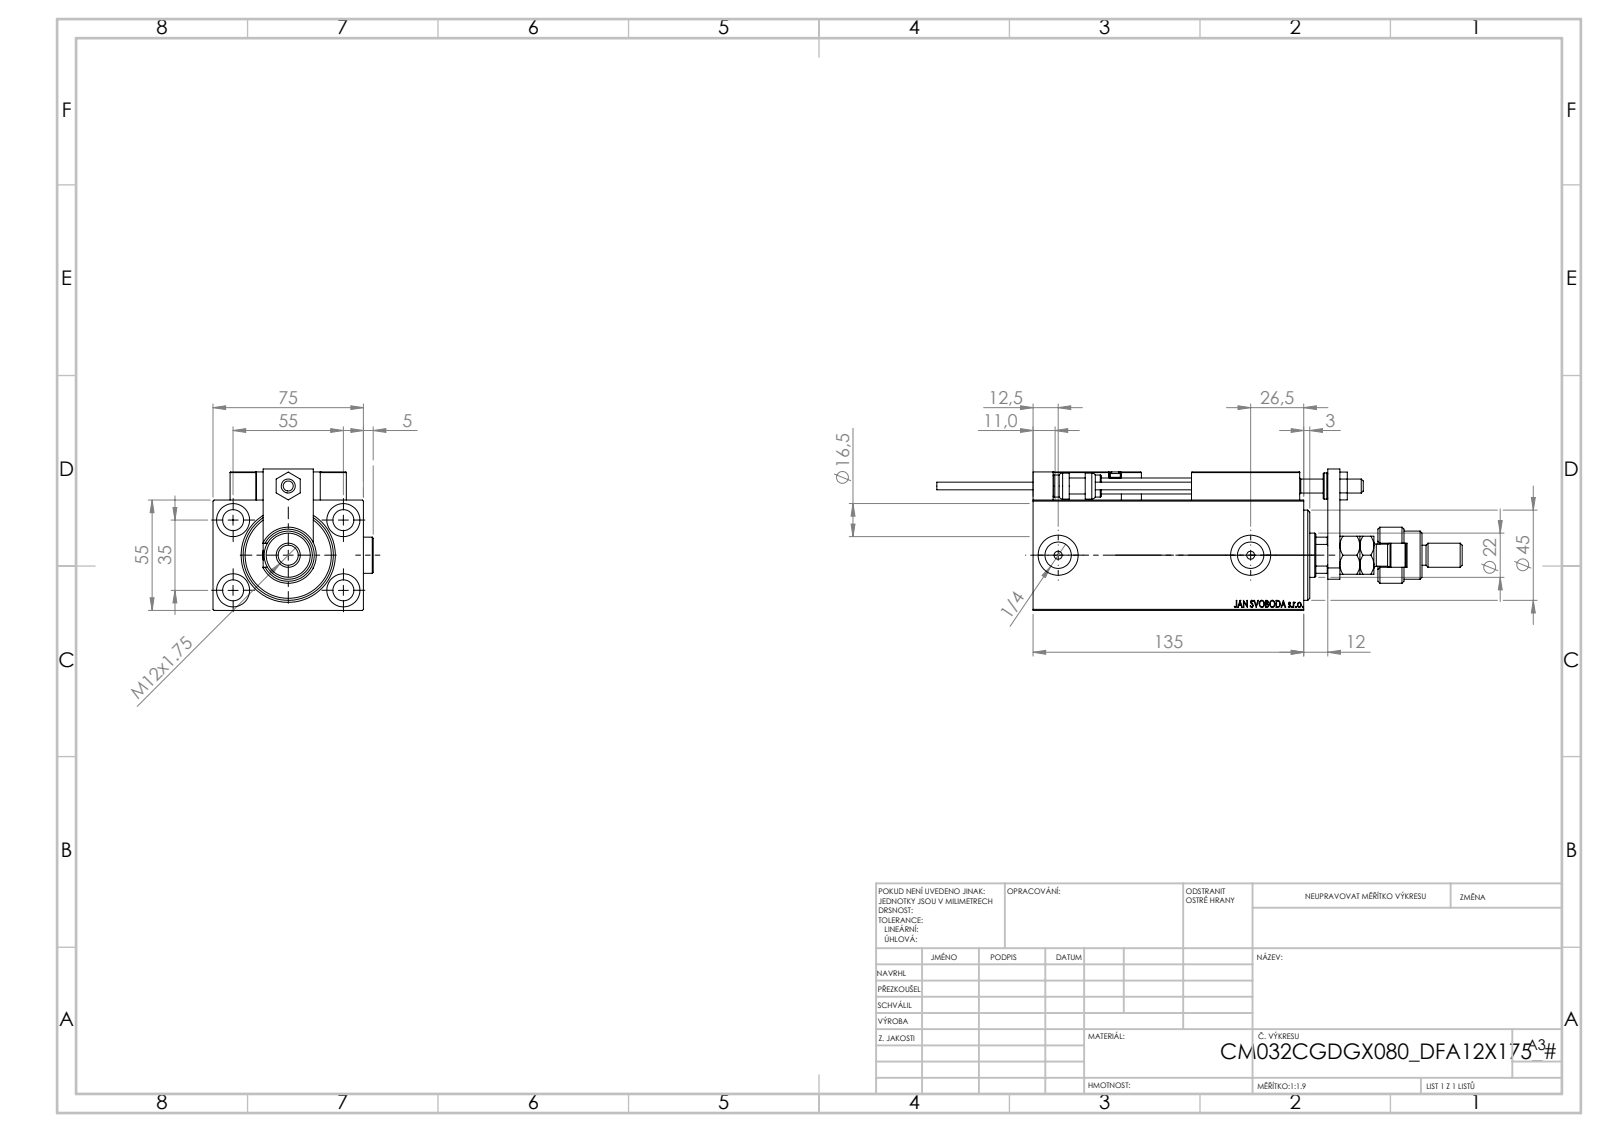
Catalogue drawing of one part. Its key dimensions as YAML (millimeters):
part_name: "V450CM_C_VCP; ALLEN BOLT D5; ALLEN BOLT D8; V450CM_VC_B (+7 more)"
step_written_by: "SolidWorks 2019 (CONFIG_CONTROL_DESIGN)"
units: millimeters
bodies: {solids: 27, faces: 1421, planar: 622, cylindrical: 217, other: 582}
overall_size: [262, 79.9, 70.5]
volume: 533833
surface_area: 129675
round_holes:
  - {diameter: 4, count: 6}
  - {diameter: 8, count: 5}
  - {diameter: 10.5, count: 5}
  - {diameter: 16.5, count: 5}
  - {diameter: 3.2, count: 4}
  - {diameter: 5, count: 2}
  - {diameter: 13.16, count: 2}
  - {diameter: 20, count: 2}
  - {diameter: 7, count: 1}
  - {diameter: 22, count: 1}
  - {diameter: 25.5, count: 1}
  - {diameter: 32, count: 1}
round_bosses_or_shafts:
  - {diameter: 18, count: 3}
  - {diameter: 11, count: 2}
  - {diameter: 5, count: 2}
  - {diameter: 3.8, count: 2}
  - {diameter: 28, count: 1}
  - {diameter: 24, count: 1}
  - {diameter: 13, count: 1}
  - {diameter: 12, count: 1}
partial_cylinders:
  - {radius: 0.3, count: 30}
  - {radius: 3, count: 2}
  - {radius: 9.75, count: 1}
  - {radius: 10.5, count: 1}
face_to_face_distances: [55, 75, 14, 12, 10, 25, 69, 18, 5, 6]
hole_center_spacings: [32.6, 11.37, 20, 29.59, 29.69, 32.33, 35, 36.06]
